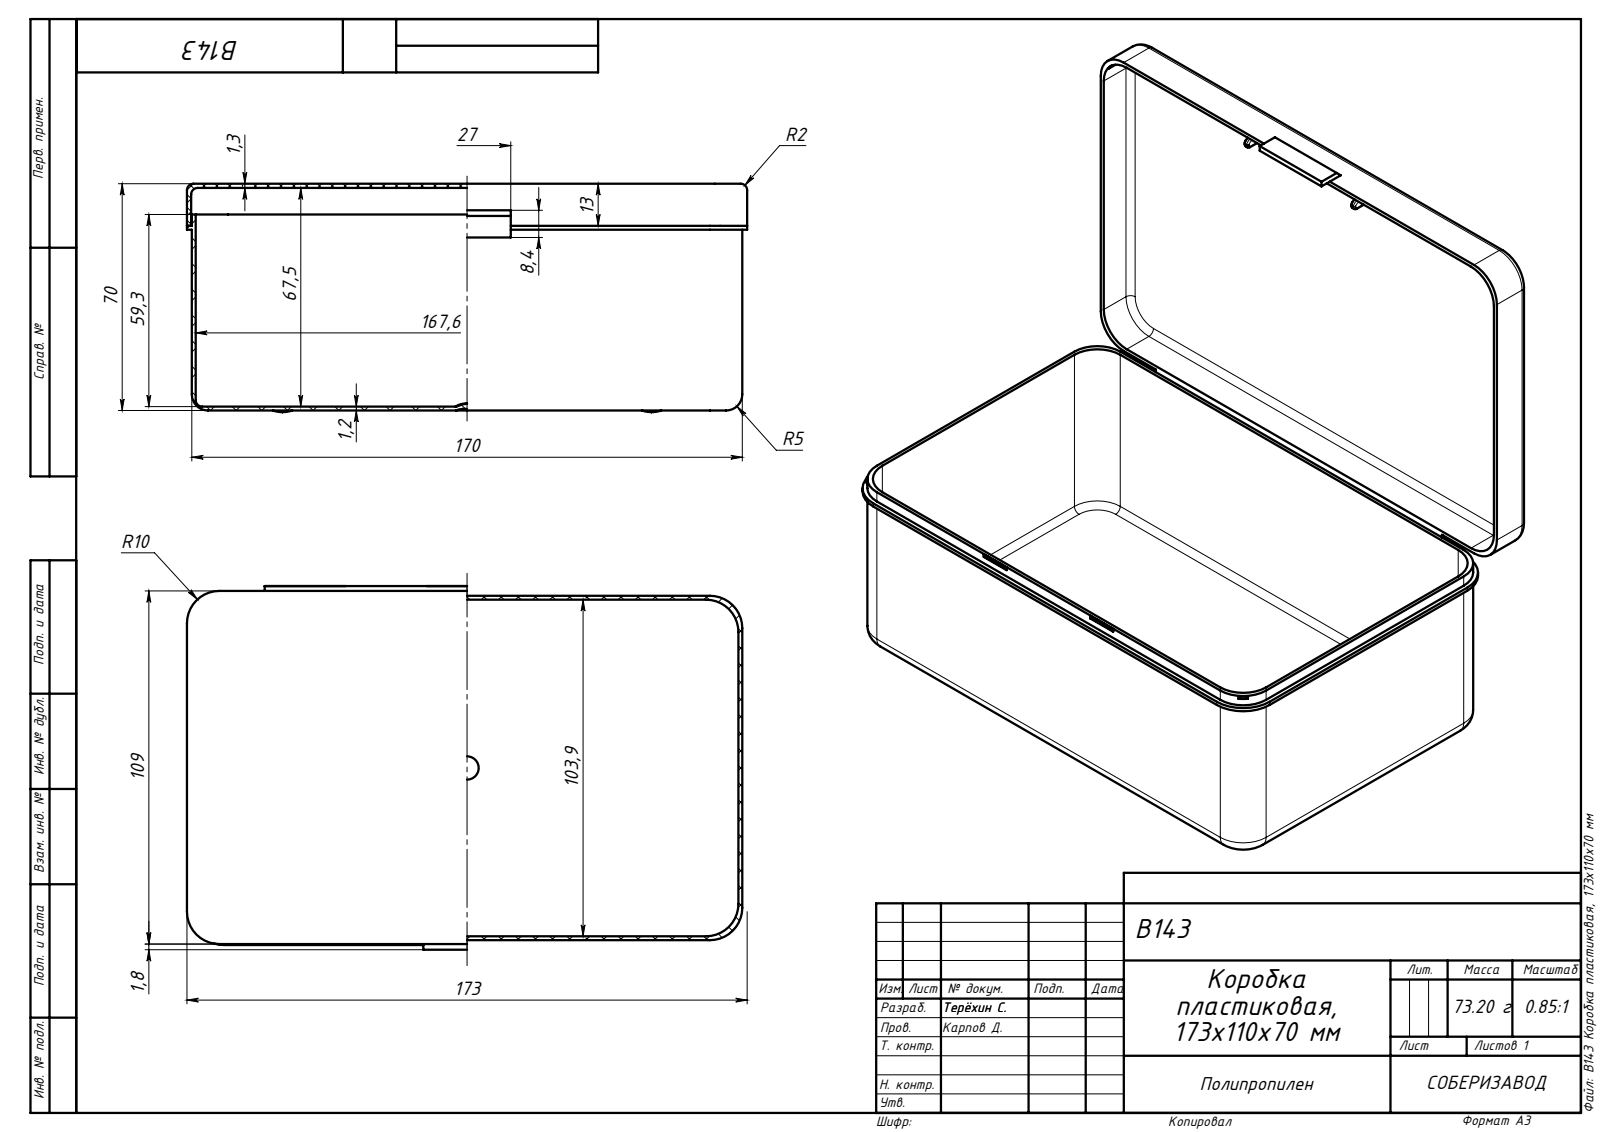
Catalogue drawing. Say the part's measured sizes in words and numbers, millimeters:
The part is named "B143 Емкость_00; B143 Коробка пластиковая, 173x110x70 мм; B143 Крышка_00". Its 3-D file was written by "SolidWorks 2019 (AUTOMOTIVE_DESIGN)". It is 5 solids with 198 faces: 72 planar, 84 cylindrical and 42 other. Overall it measures 173 by 112.25 by 70.5 millimeters. Its volume is 92 698 cubic millimeters and its surface area 150 869 square millimeters. Partial cylindrical surfaces (rounded edges, fillets, slot ends): 27 of radius 0.5, 16 of radius 10, 12 of radius 2, 4 of radius 5, 4 of radius 11.5, 2 of radius 0.6, 2 of radius 10.3, 1 of radius 1. The main face-to-face distances are 1.2, 1.3, 105.1, 67.5, 68.8, 68.7, 70, 106.3, 168.8, 103.9.
